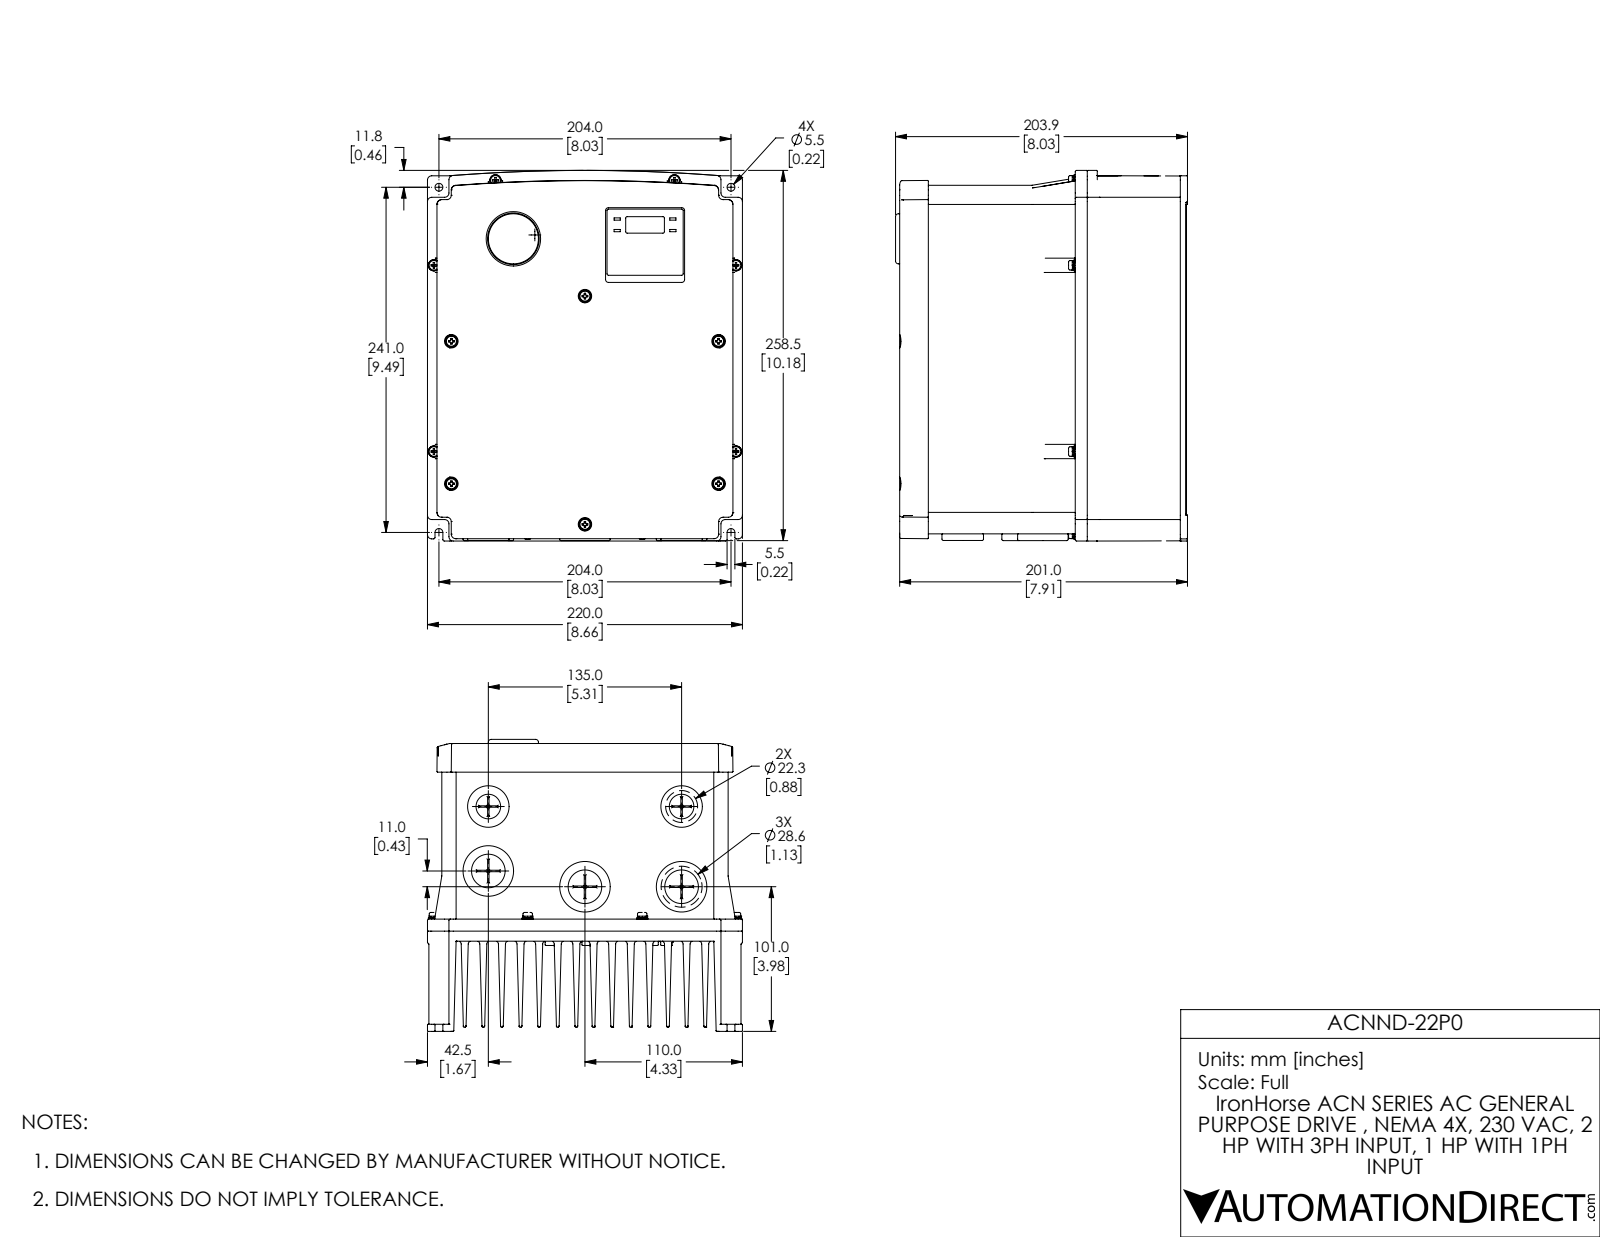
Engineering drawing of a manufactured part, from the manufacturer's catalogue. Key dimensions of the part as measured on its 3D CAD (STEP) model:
Part name (STEP PRODUCT): total_ig7_ip66_037_v2_asm Red 1 EXT1B w Non PDS KNOB 1 m1c
STEP written by: SolidWorks 2017 (AUTOMOTIVE_DESIGN)
Units: inches
Bodies: 18 solids, 3306 faces (1087 planar, 1034 cylindrical, 1185 other)
Overall size (bounding box): 10.188 × 8.661 × 8.028
Volume: 455.6 in³ · Surface area: 1 299 in²
Round holes (diameter × count): ⌀0.157 ×18, ⌀0.177 ×8, ⌀0.118 ×6, ⌀0.331 ×6, ⌀0.925 ×3, ⌀1.126 ×3, ⌀1.272 ×3, ⌀0.142 ×2, ⌀0.217 ×2, ⌀0.677 ×2, ⌀0.878 ×2, ⌀1.024 ×2
Round bosses / shafts (diameter × count): ⌀0.311 ×8, ⌀0.264 ×8, ⌀0.315 ×6, ⌀1.39 ×3, ⌀1.098 ×3, ⌀1.142 ×2, ⌀0.85 ×2, ⌀0.551 ×1
Partial cylindrical surfaces — rounded edges, fillets, slot ends (radius × count): R0.02 ×275, R0.079 ×77, R0.118 ×62, R0.039 ×46, R0.008 ×25, R0.197 ×8, R0.167 ×5, R0.157 ×4
Main face-to-face distances: 0.512, 1.024, 1.535, 3.543, 2.047, 4.055, 3.031, 4.567, 2.52, 2.559
Hole centre spacings: 2.835, 5.902, 5.177, 5.696, 1.007, 1.567, 1.597, 2.141
